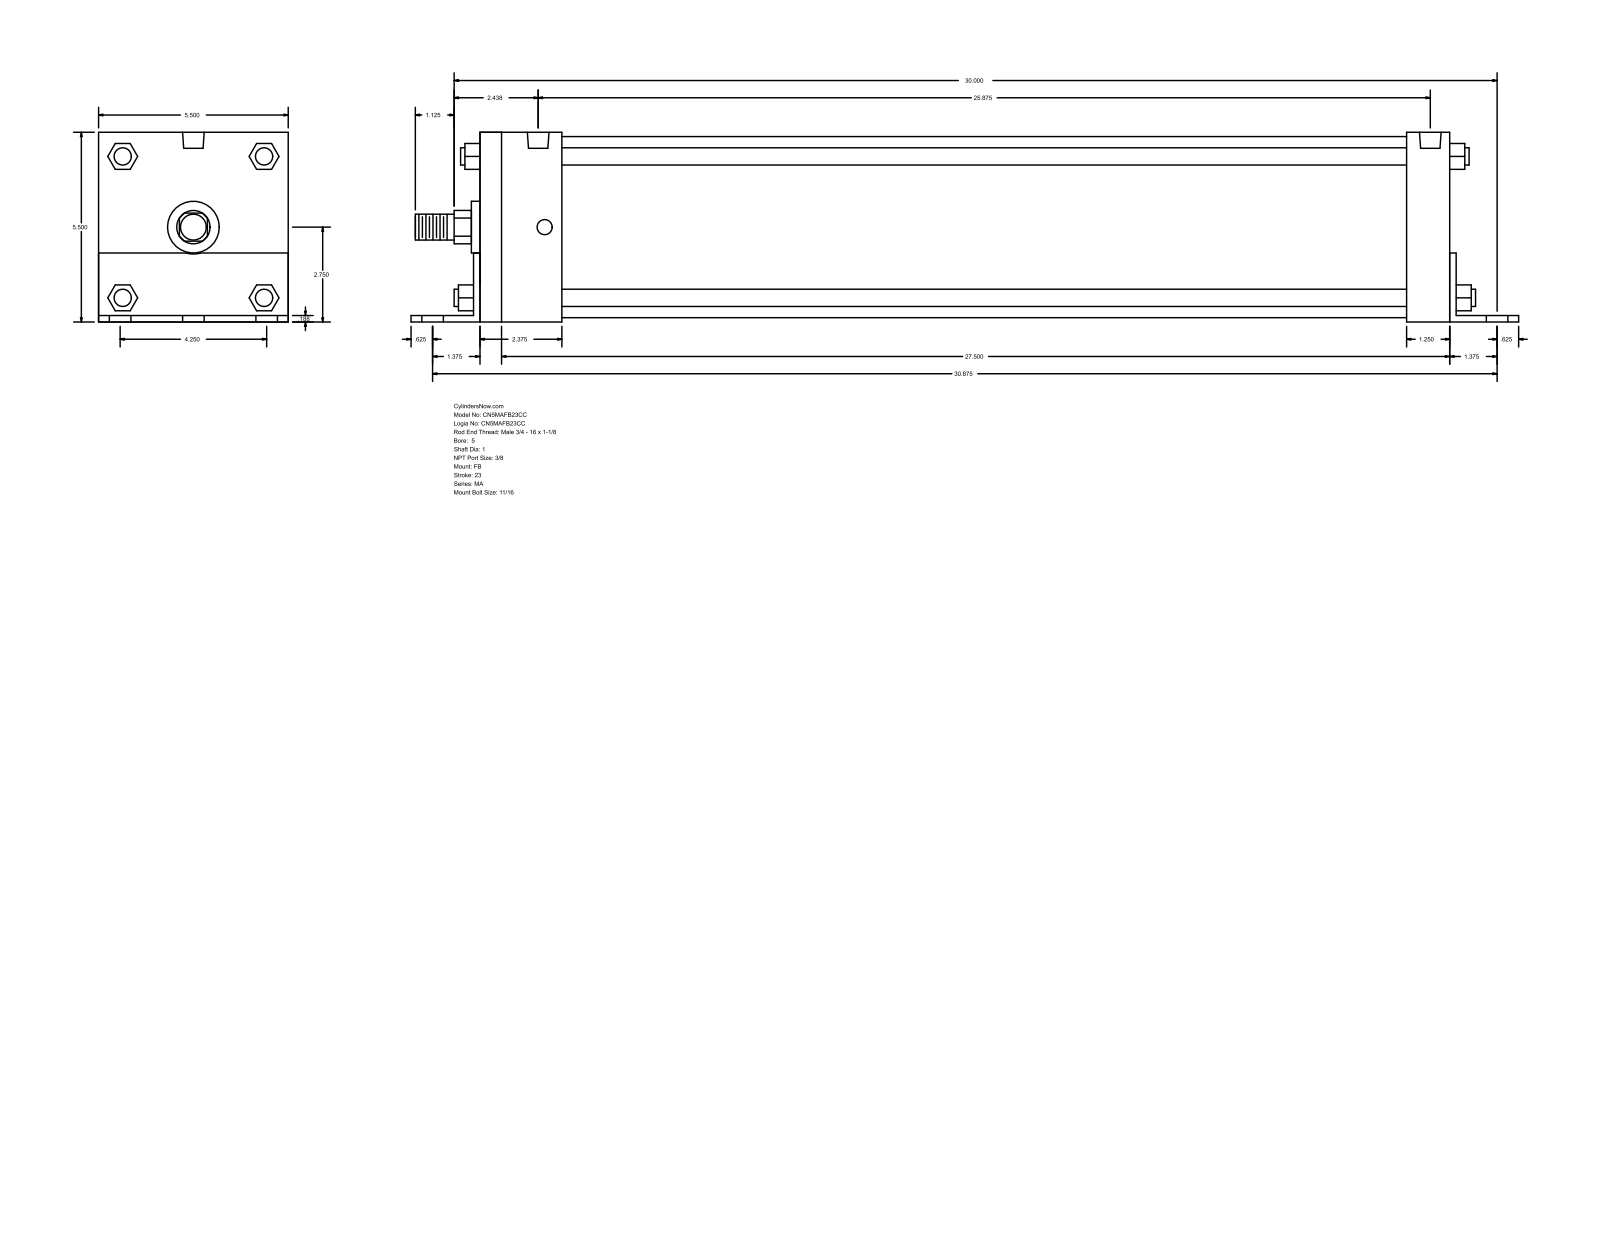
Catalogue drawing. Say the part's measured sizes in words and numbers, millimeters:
The part is named "MA_FB__0500_1". Its 3-D file was written by "GSSL Pune (CONFIG_CONTROL_DESIGN)". It is 0 solids with 140 faces: 105 planar, 35 cylindrical and 0 other. Overall it measures 815.98 by 139.75 by 139.7 millimeters. Round holes: 6 of diameter 17.46, 4 of diameter 11.11, 2 of diameter 15.93. Round bosses or shafts: 4 of diameter 12.7, 1 of diameter 133.35, 1 of diameter 38.1, 1 of diameter 25.4, 1 of diameter 19.05. Partial cylindrical surfaces (rounded edges, fillets, slot ends): 1 of radius 12.29, 1 of radius 19.81. The main face-to-face distances are 139.7, 4.76, 139.75, 4.71, 134.99, 714.37, 4.77, 719.14, 719.13, 723.9. The hole center spacings are 53.98, 786.09, 784.23, 4.76, 73.04, 76.33, 94.68, 98.63.
